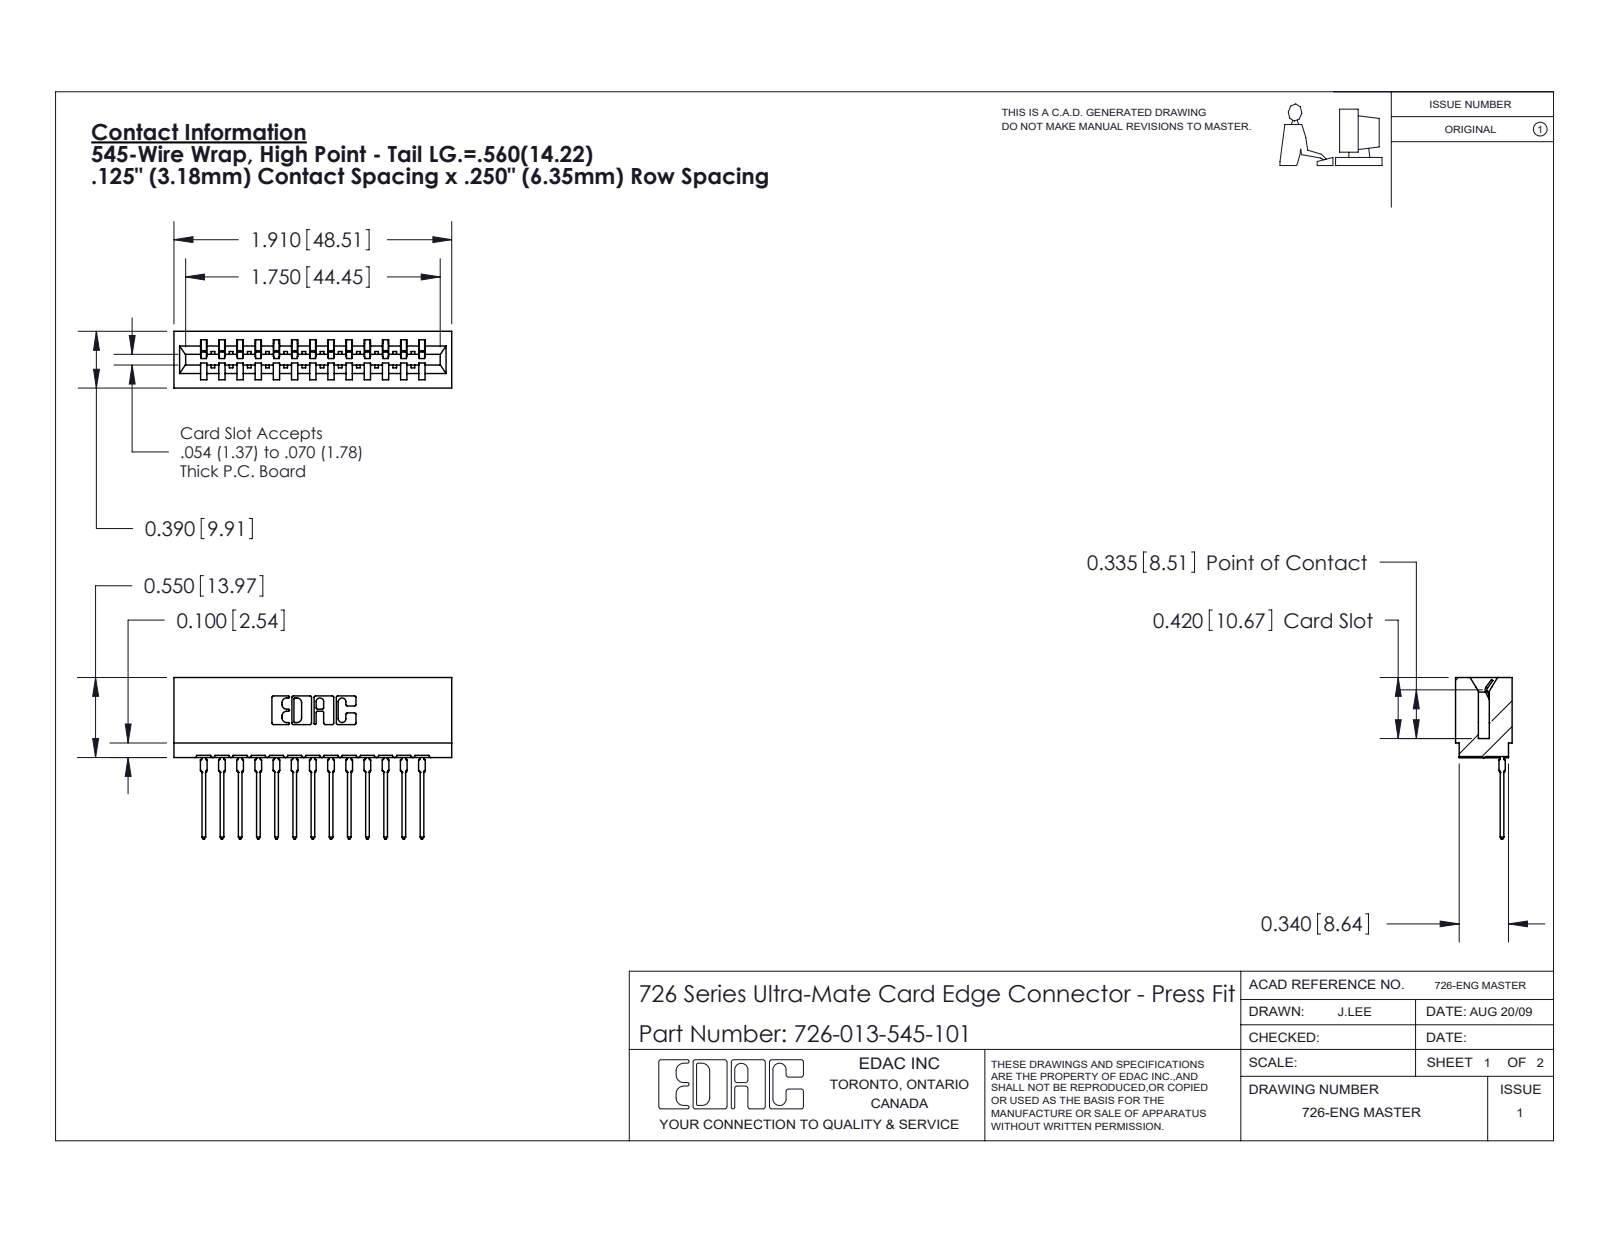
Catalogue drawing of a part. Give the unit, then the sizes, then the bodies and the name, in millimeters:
Units: millimetres
Overall size (bounding box): 48.5 × 28.2 × 9.9
Partial cylindrical surfaces — rounded edges, fillets, slot ends (radius × count): R0.5 ×26, R0.3 ×22, R0.4 ×14, R0.2 ×6, R0.8 ×6, R0.1 ×4, R0.3 ×4, R0.7 ×3
Main face-to-face distances: 6.4, 1.4, 8.5, 12.7, 19.1, 9.9, 3.2, 13.8, 3.2, 0.6
Volume: 4 540 mm³ · Surface area: 6 677 mm²
Bodies: 14 solids, 1501 faces (874 planar, 289 cylindrical, 338 other)
Part name (STEP PRODUCT): 746-292-001_545; 726 Part_.515 Slot Depth - 01; 726-013-545-101
STEP written by: SolidWorks 2020 (CONFIG_CONTROL_DESIGN)
